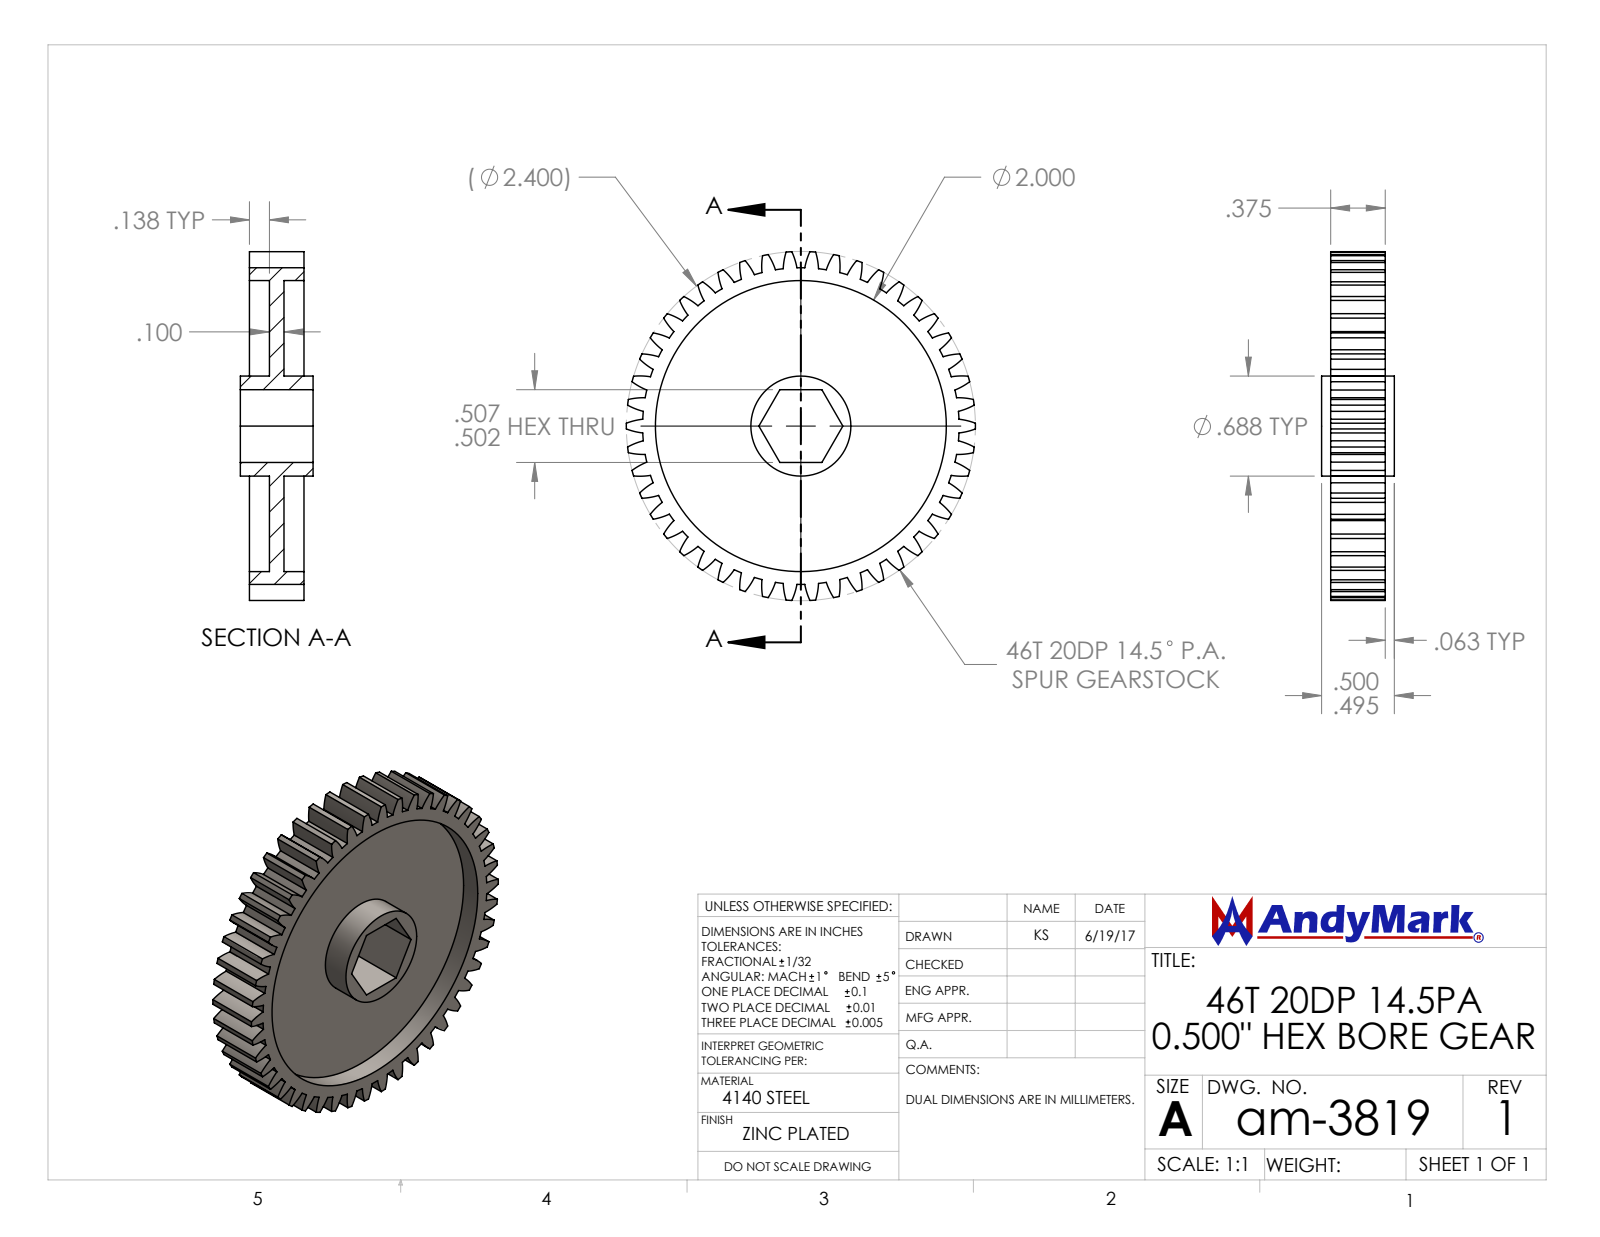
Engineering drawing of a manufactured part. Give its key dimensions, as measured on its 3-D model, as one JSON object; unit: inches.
{"part_name": "am-3819 46T 20DP 500hex 375 FW", "step_written_by": "SolidWorks 2021 (CONFIG_CONTROL_DESIGN)", "units": "inches", "bodies": {"solids": 1, "faces": 305, "planar": 12, "cylindrical": 197, "other": 96}, "overall_size": [2.4, 2.397, 0.5], "volume_in3": 0.733, "surface_area_in2": 16.69, "round_holes": [[2, 1]], "round_bosses_or_shafts": [[0.75, 1]], "partial_cylinders_radius": [[0.46, 92], [1.088, 1], [1.2, 1]], "face_to_face_distances": [0.1, 0.238, 0.138, 0.137, 0.237, 0.375, 0.5, 0.2, 0.3, 0.063]}
